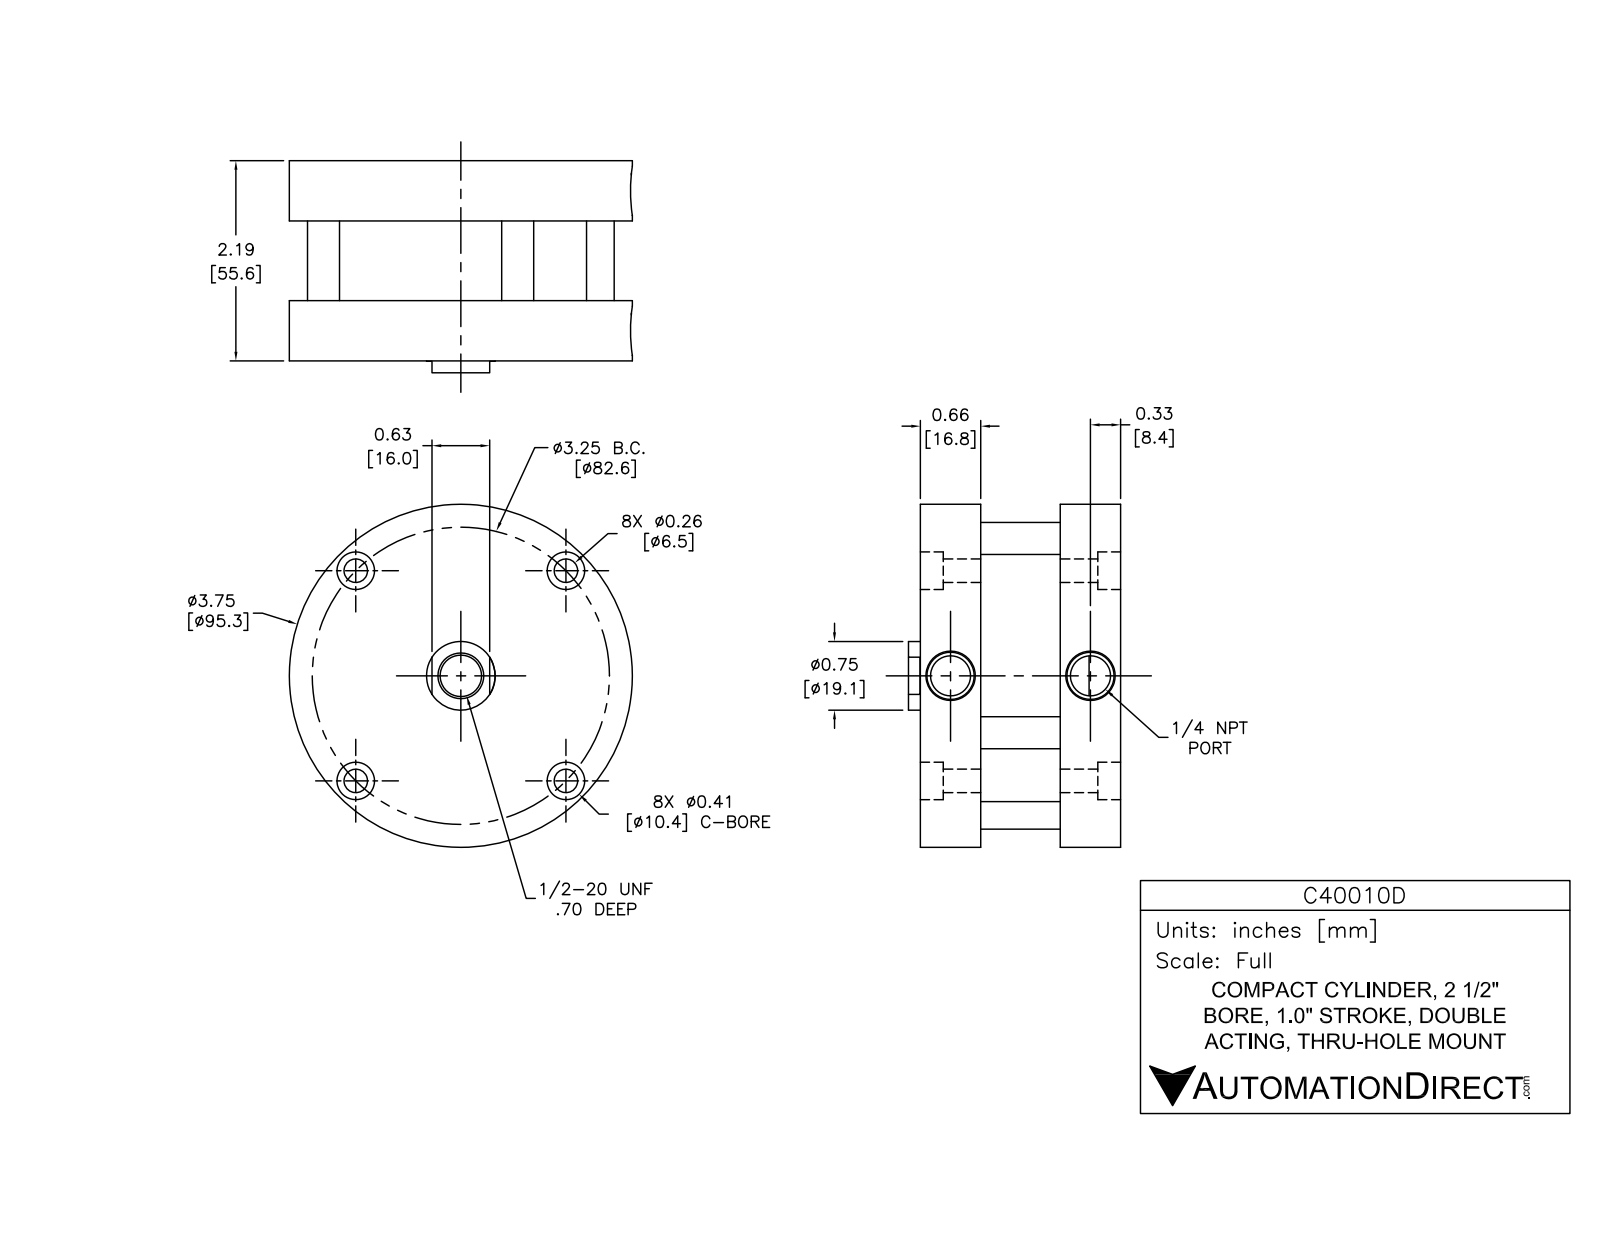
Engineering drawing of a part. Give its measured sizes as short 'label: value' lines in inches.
name: C40010D; C40010D-FO1_BM_heads (2); C40010D-FO1_BM_heads; C40010D-FO1_BM_tube (+3 more)
written by: SolidWorks 2014 (AUTOMOTIVE_DESIGN)
unit: in
bodies: 9 solids, 165 faces (49 planar, 98 cylindrical, 18 other)
size: 3.75 × 3.75 × 2.32
volume: 14.71 in³; area: 123 in²
holes: 4× ⌀0.225, 4× ⌀0.281, 4× ⌀0.406, 2× ⌀0.218, 1× ⌀0.446, 1× ⌀0.75, 1× ⌀0.752, 1× ⌀2.5, 1× ⌀2.639
bosses: 4× ⌀0.45, 4× ⌀0.225, 1× ⌀3.75
face distances: 0.387, 1.803, 2.19, 1.416, 1.53, 1.143, 0.273, 0.66, 0.66, 0.273
hole spacings: 0.48, 1.625, 1.625, 1.933, 2.298, 2.298, 2.613, 3.215
